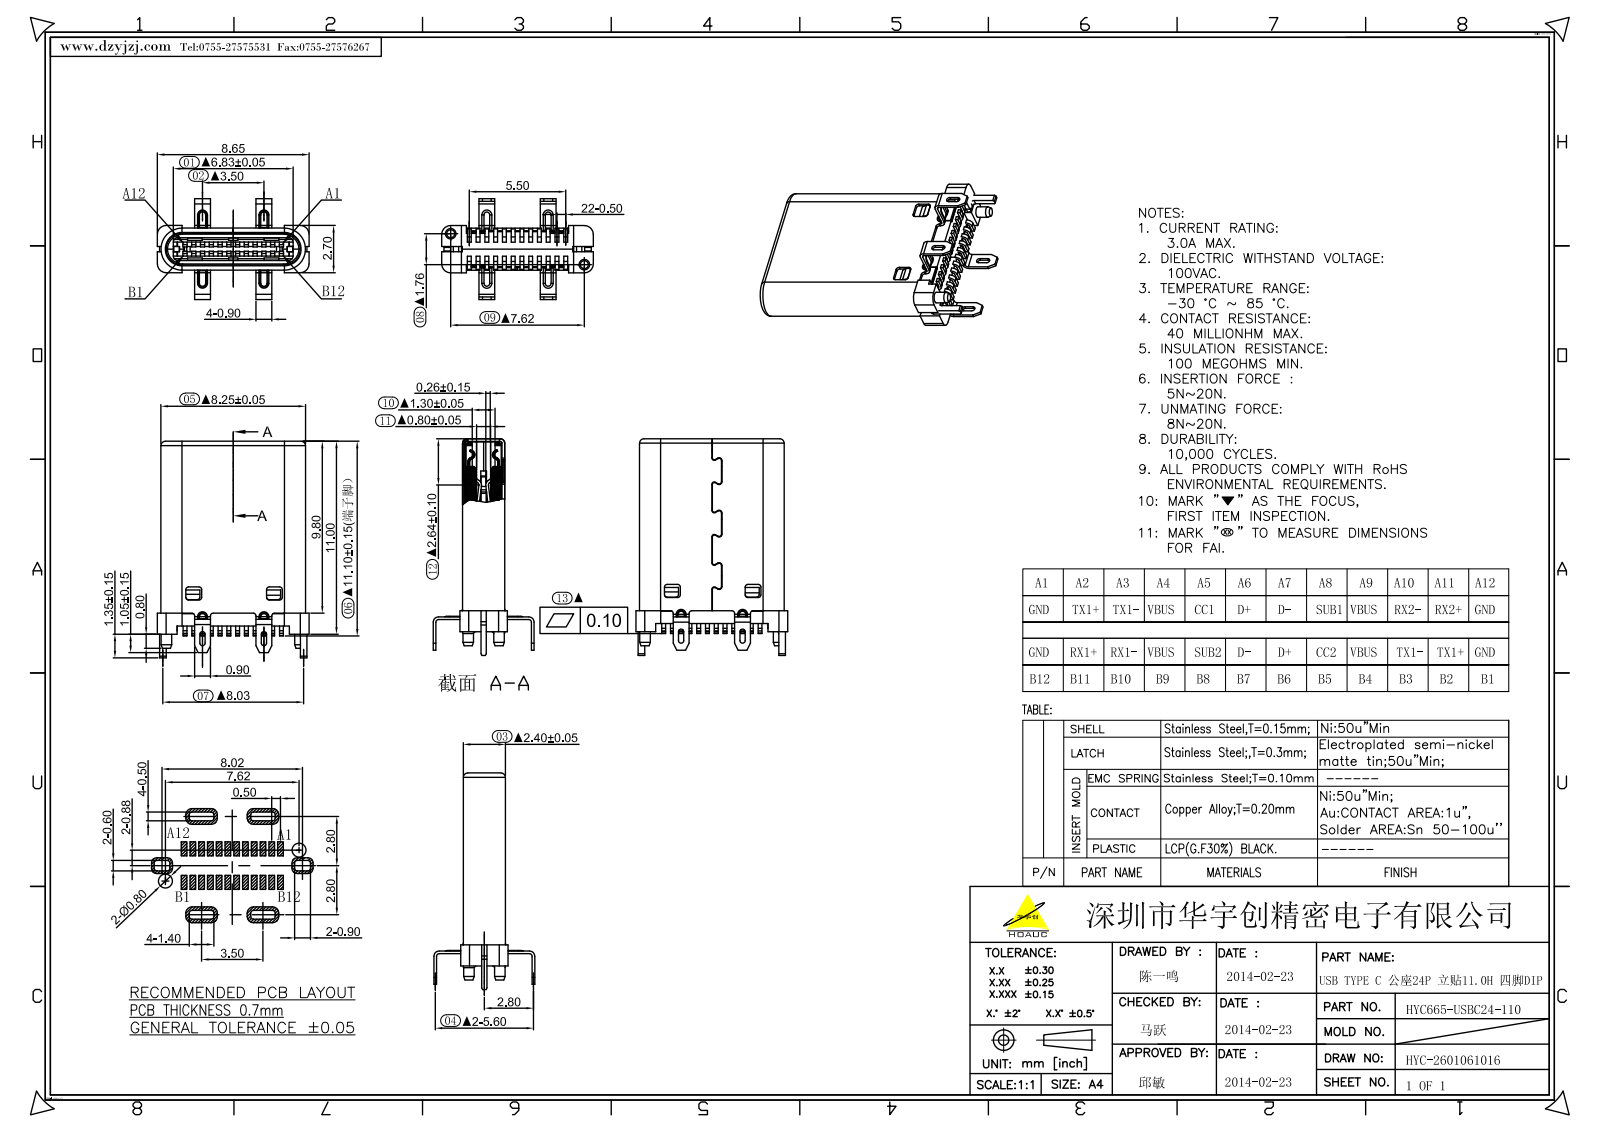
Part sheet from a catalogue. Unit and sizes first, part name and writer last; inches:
Units: inches
Overall size (bounding box): 0.486 × 0.341 × 0.226
Round bosses / shafts (diameter × count): ⌀0.024 ×2
Partial cylindrical surfaces — rounded edges, fillets, slot ends (radius × count): R0.006 ×36, R0.005 ×16, R0.004 ×14, R0.005 ×12, R0.01 ×12, R0.004 ×6, R0.006 ×6, R0.012 ×6
Main face-to-face distances: 0.094, 0.031, 0.041, 0.022, 0.063, 0.02, 0.073, 0.039, 0.059, 0.079
Volume: 0.01 in³ · Surface area: 0.767 in²
Bodies: 1 solid, 1376 faces (1014 planar, 306 cylindrical, 56 other)
Part name (STEP PRODUCT): TANPIAN-PLASTIC_1_2__2_23_1_1_8
STEP written by: CREO PARAMETRIC BY PTC INC, 2022073 (CONFIG_CONTROL_DESIGN)
